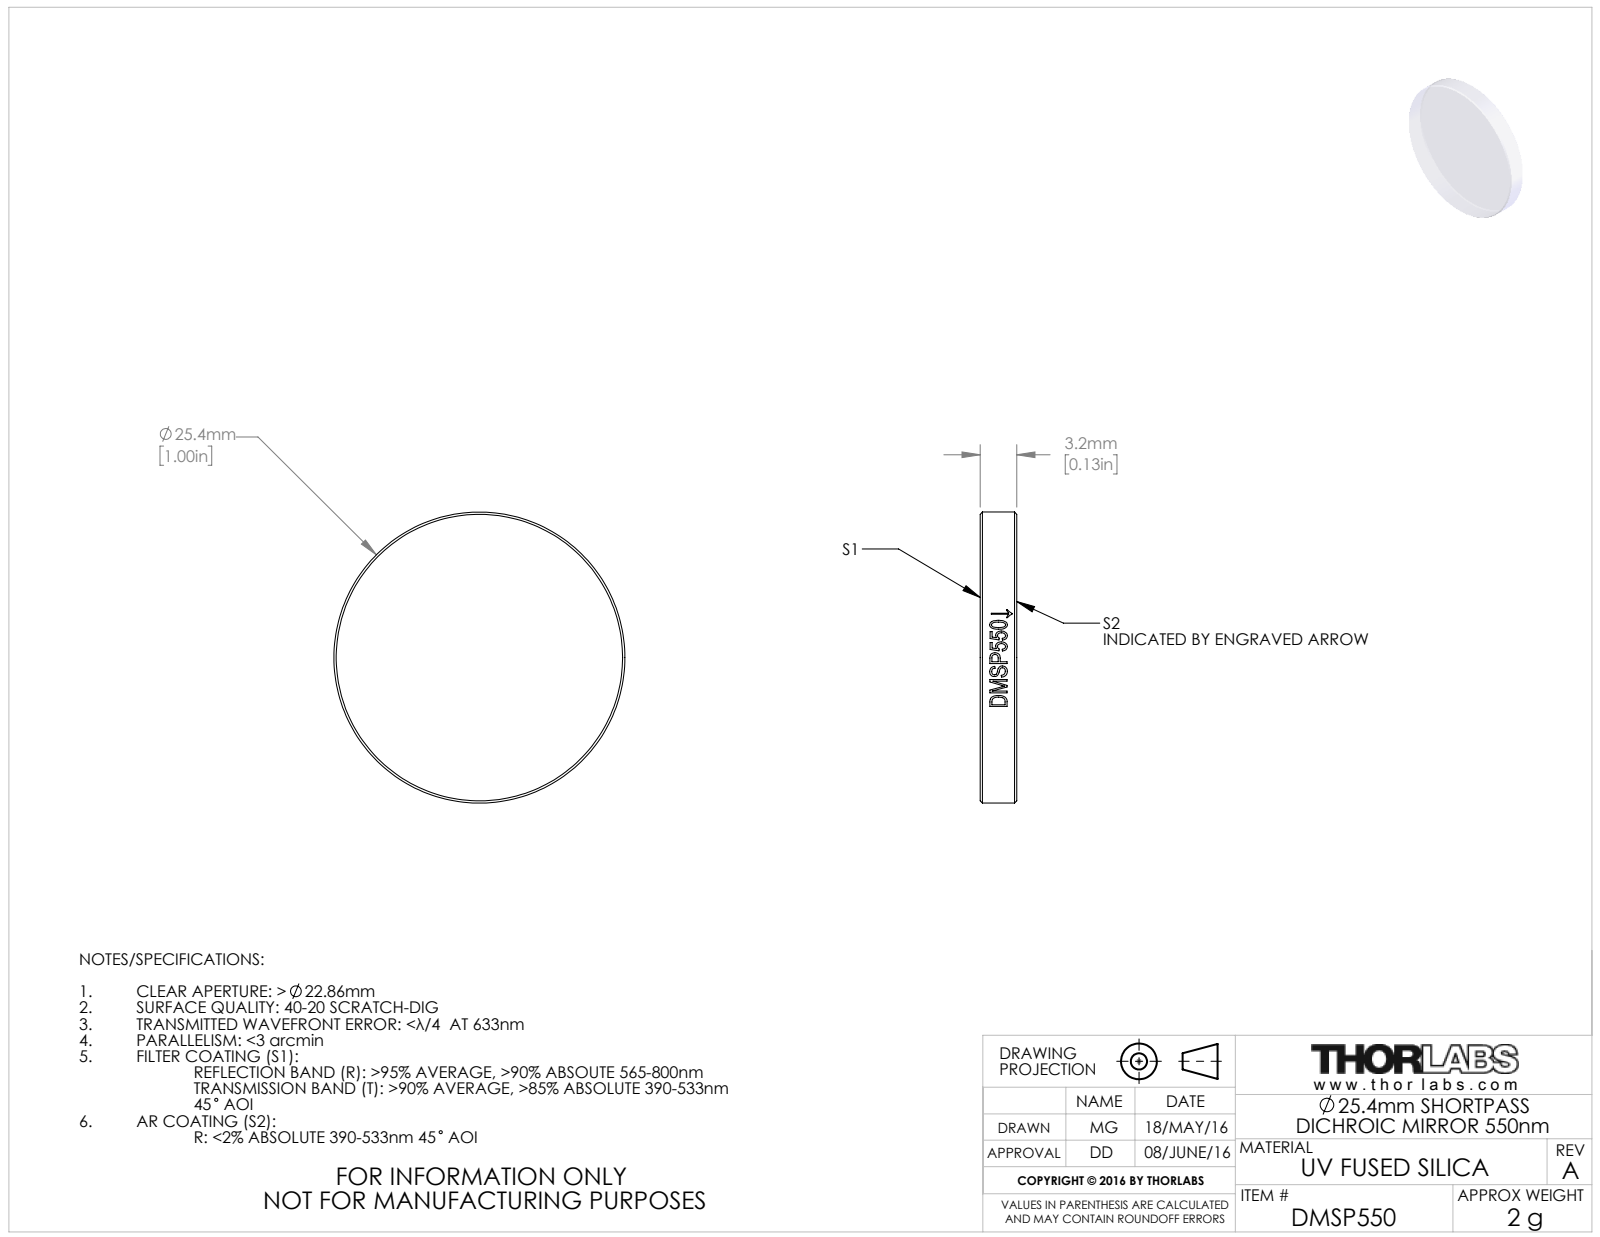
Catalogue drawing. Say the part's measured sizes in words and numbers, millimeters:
The part is named "TTN045149-E0W". Its 3-D file was written by "SolidWorks 2016 (CONFIG_CONTROL_DESIGN)". It is 1 solid with 19 faces: 2 planar, 13 cylindrical and 4 other. Overall it measures 25.4 by 25.4 by 3.2 millimeters. Its volume is 1 618 cubic millimeters and its surface area 1 250 square millimeters. Round bosses or shafts: 1 of diameter 25.4. The main face-to-face distances are 3.2.
